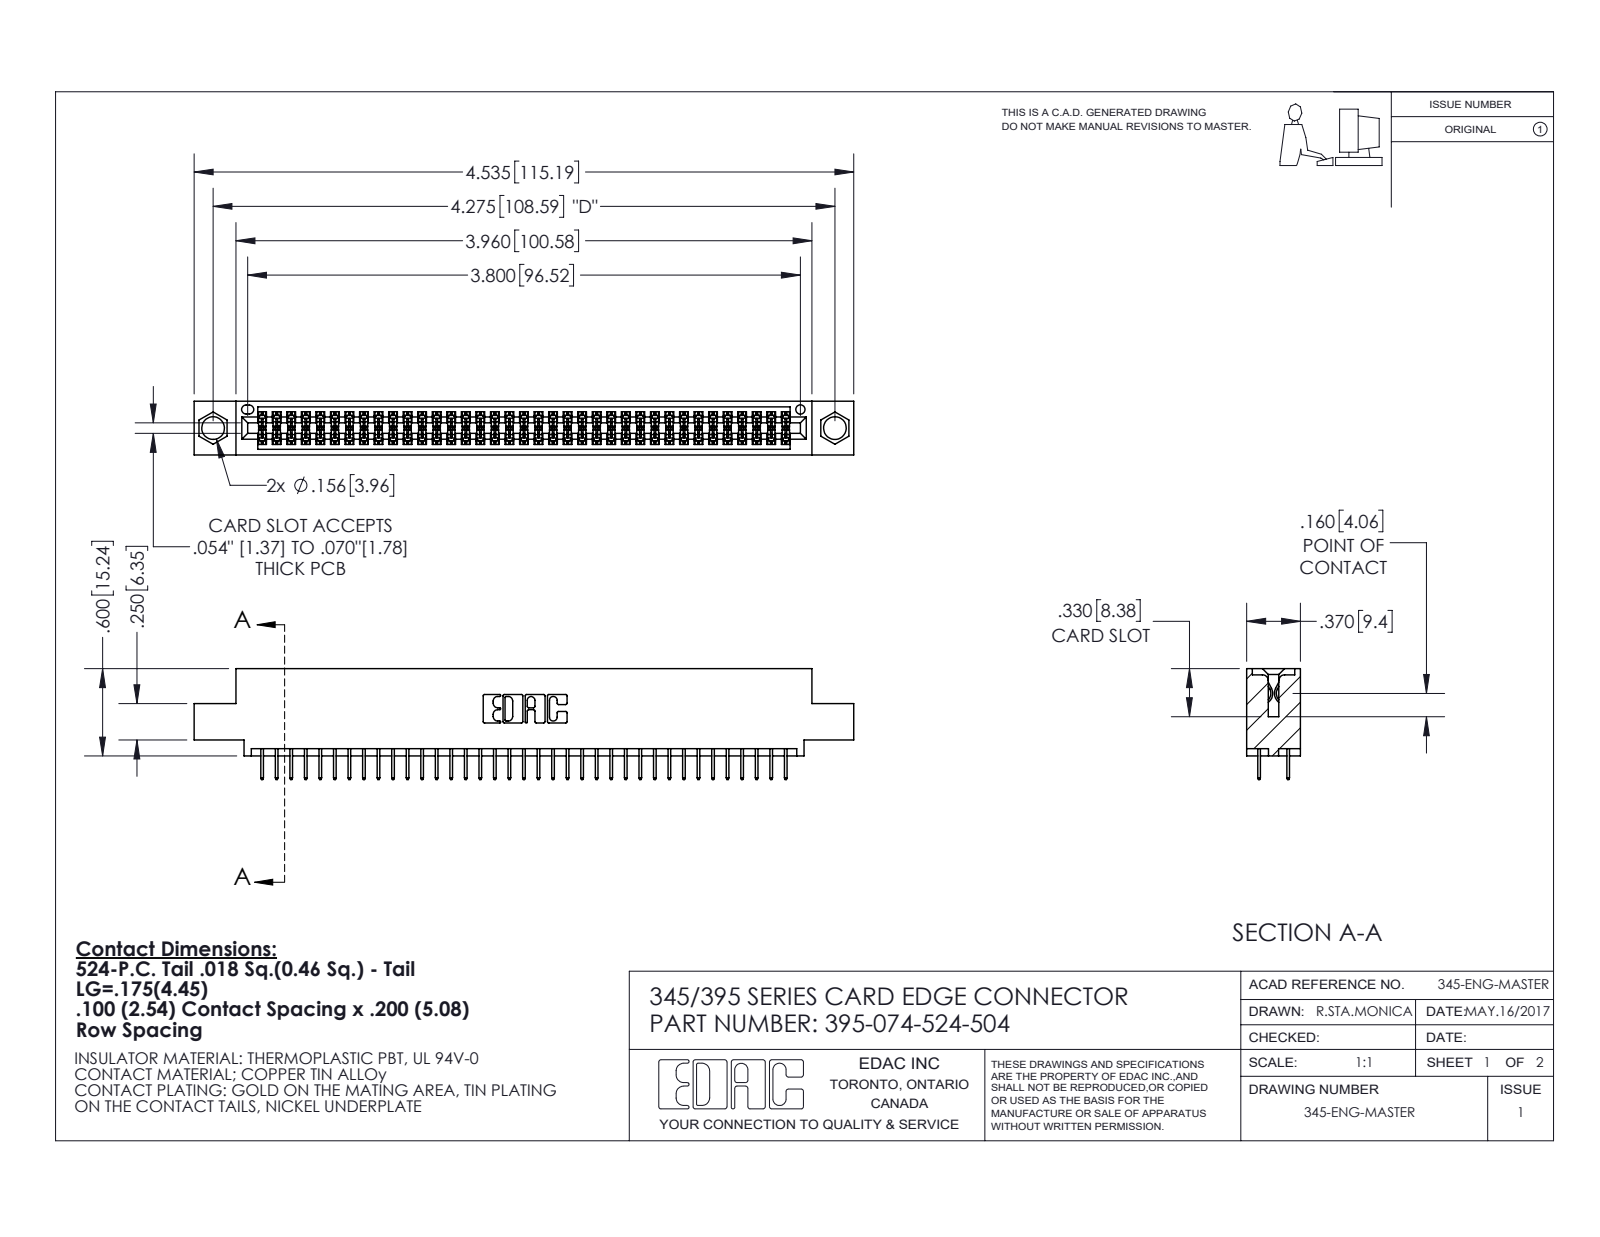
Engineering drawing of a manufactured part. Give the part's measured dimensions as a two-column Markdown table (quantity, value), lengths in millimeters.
| quantity | value |
| --- | --- |
| part name | 345 Part_0.110 Offset - 0.156 Dia-TI; 395-074-524-504; 345-292-001_345-293-124 |
| STEP written by | SolidWorks 2020 (CONFIG_CONTROL_DESIGN) |
| units | millimeters |
| bodies | 75 solids, 4140 faces (2984 planar, 1156 cylindrical, 0 other) |
| overall size | 115.2 × 19.4 × 9.4 |
| volume | 10 800 mm³ |
| surface area | 15 590 mm² |
| round holes (diameter × count) | 4 × 2, 1.6 × 1 |
| partial cylindrical surfaces (radius × count) | 0.2 × 111, 0.3 × 22, 0.2 × 6, 0.8 × 6, 0.7 × 3, 0.4 × 2, 0.5 × 2, 0.6 × 2 |
| main face-to-face distances | 1.8, 7.6, 5.1, 9.4, 2.5, 6.9, 0.6, 5.7, 1.8, 4.4 |
| hole center spacings | 6.9, 102.6, 108.6 |
